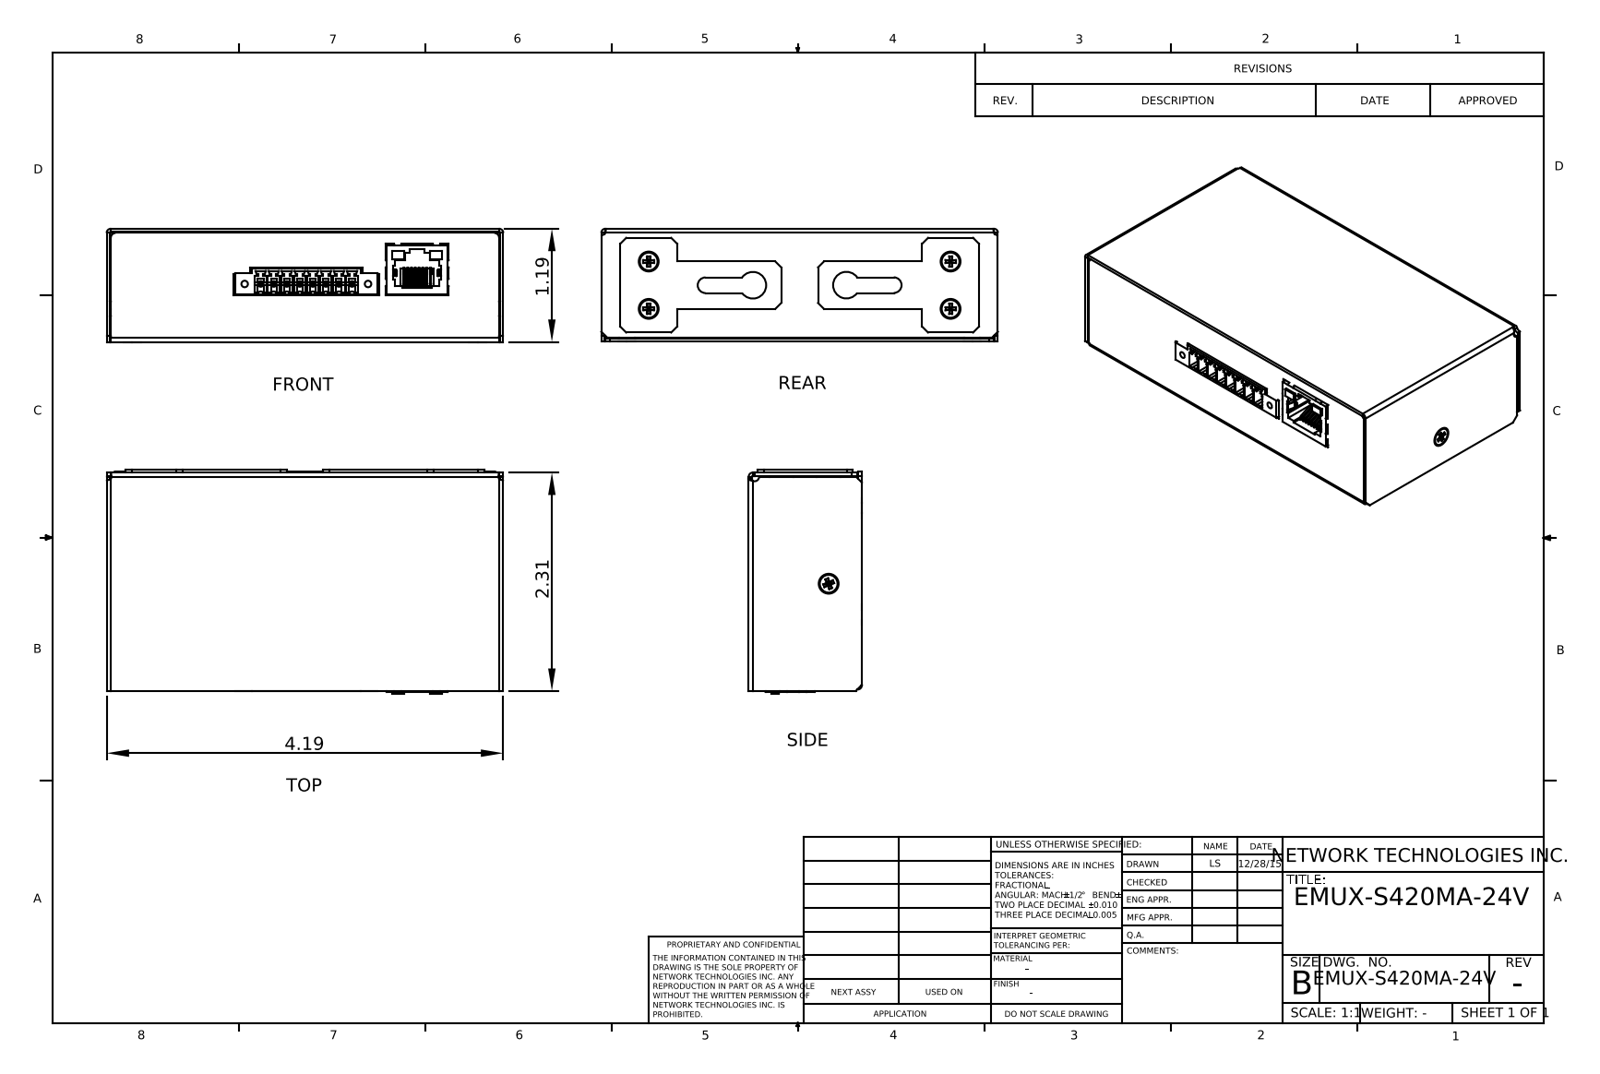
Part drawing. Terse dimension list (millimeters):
name: EMUX-S420MA-24V; HW4033-SCRW#4-40x.25-BUT-TORX-T8-ZN_90022A110; HW5127 CR-FHMS 0.112-40x0.188x0.188_CR-FHMS 0.112-40x0.188x0.188-C; HW4120_PEM S-440-0 ZI--N (+7 more)
written by: SolidWorks 2011 (AUTOMOTIVE_DESIGN)
unit: mm
bodies: 21 solids, 1856 faces (1214 planar, 490 cylindrical, 152 other)
size: 106.38 × 60.13 × 30.33
volume: 31 753 mm³; area: 64 999 mm²
holes: 12× ⌀1.65, 8× ⌀1.57, 6× ⌀2.26, 6× ⌀4.19, 5× ⌀1.78, 5× ⌀4.75, 4× ⌀2.84, 4× ⌀3.17, 3× ⌀1.5, 2× ⌀1.75, 2× ⌀2.41, 2× ⌀3.38
bosses: 24× ⌀0.46, 8× ⌀1.5, 5× ⌀5.33, 4× ⌀6.35, 4× ⌀3.84, 3× ⌀2.84, 2× ⌀5.56, 2× ⌀3.98
rounds: 16× R0.75, 12× R0.17, 12× R0.96, 9× R1.27, 8× R0.81, 6× R0.2, 6× R1.02, 6× R1.07
face distances: 0.87, 0.86, 30.33, 29.46, 28.6, 29.47, 12.73, 11.87, 16.73, 17.6
hole spacings: 2.05, 3.5, 2.03, 3.53, 7, 28.65, 53.42, 5.38
